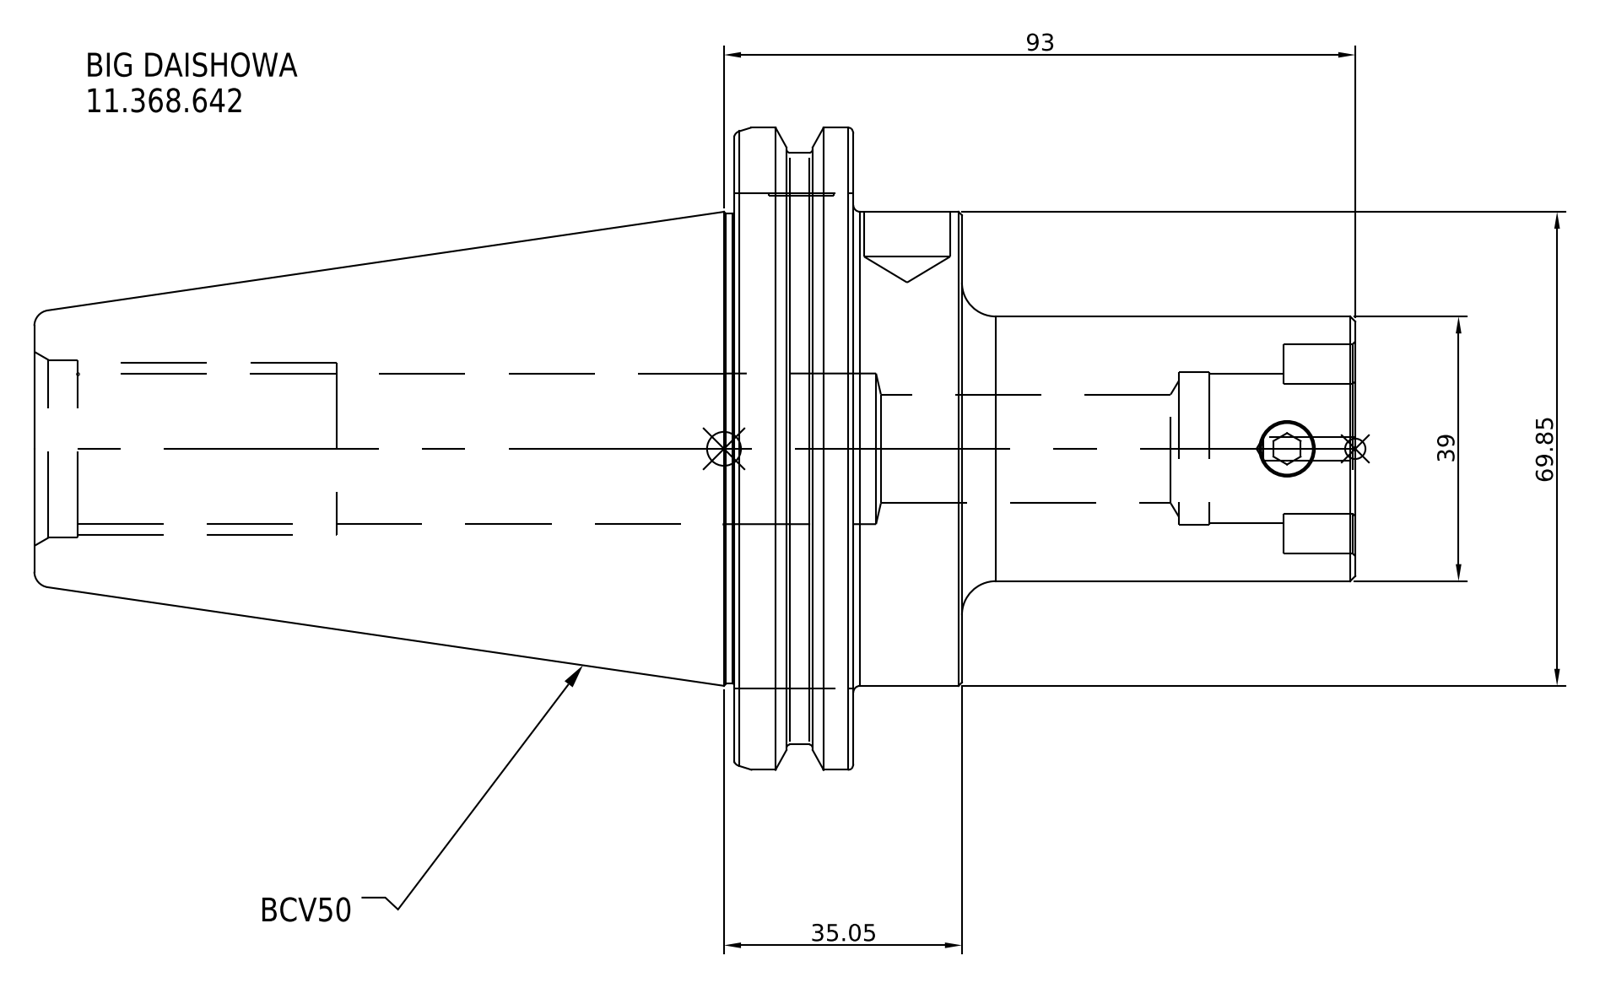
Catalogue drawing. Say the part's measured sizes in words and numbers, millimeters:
The part is named "11.368.642". Its 3-D file was written by "SolidWorks 2021 (CONFIG_CONTROL_DESIGN)". It is 1 solid with 16 faces: 7 planar, 6 cylindrical and 3 other. Overall it measures 194.6 by 98.43 by 98.43 millimeters. Its volume is 511 767 cubic millimeters and its surface area 48 079 square millimeters. Round bosses or shafts: 1 of diameter 98.43, 1 of diameter 91.29, 1 of diameter 69.85, 1 of diameter 39. The main face-to-face distances are 17.55, 15.95, 33.5, 136.6, 120.65, 103.1, 58, 73.95, 91.5, 194.6.
